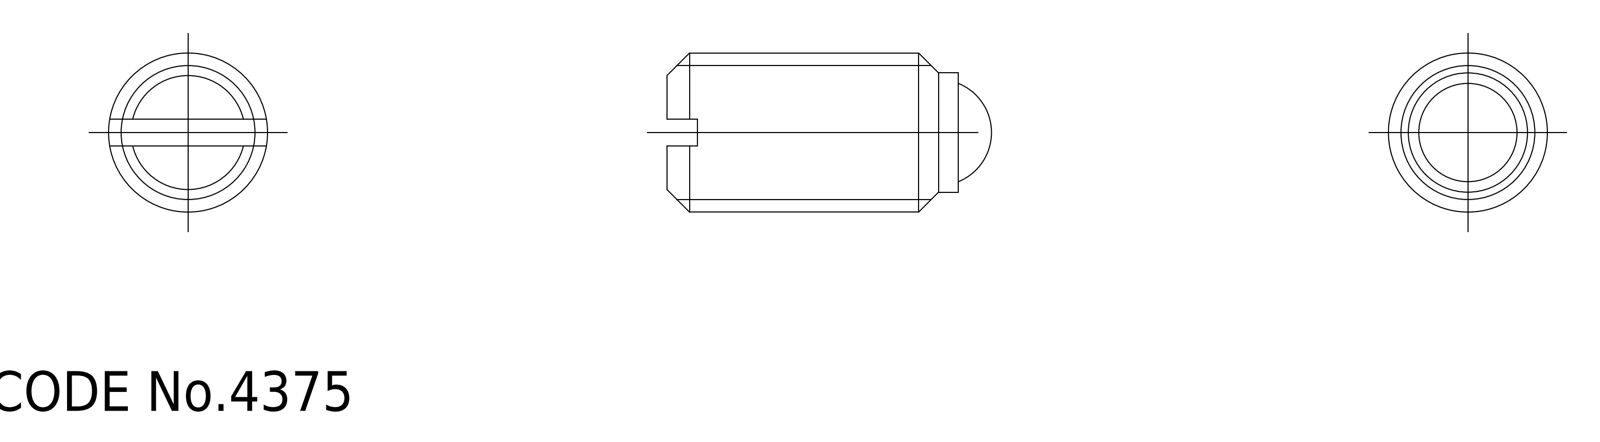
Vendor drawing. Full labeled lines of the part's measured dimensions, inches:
Part name (STEP PRODUCT): ball; PBF_12_KN_13953_36
STEP written by: CADfix (AUTOMOTIVE_DESIGN)
Units: inches
Bodies: 2 solids, 19 faces (0 planar, 0 cylindrical, 19 other)
Overall size (bounding box): 0.965 × 0.472 × 0.472
Volume: 0.127 in³ · Surface area: 2.244 in²
